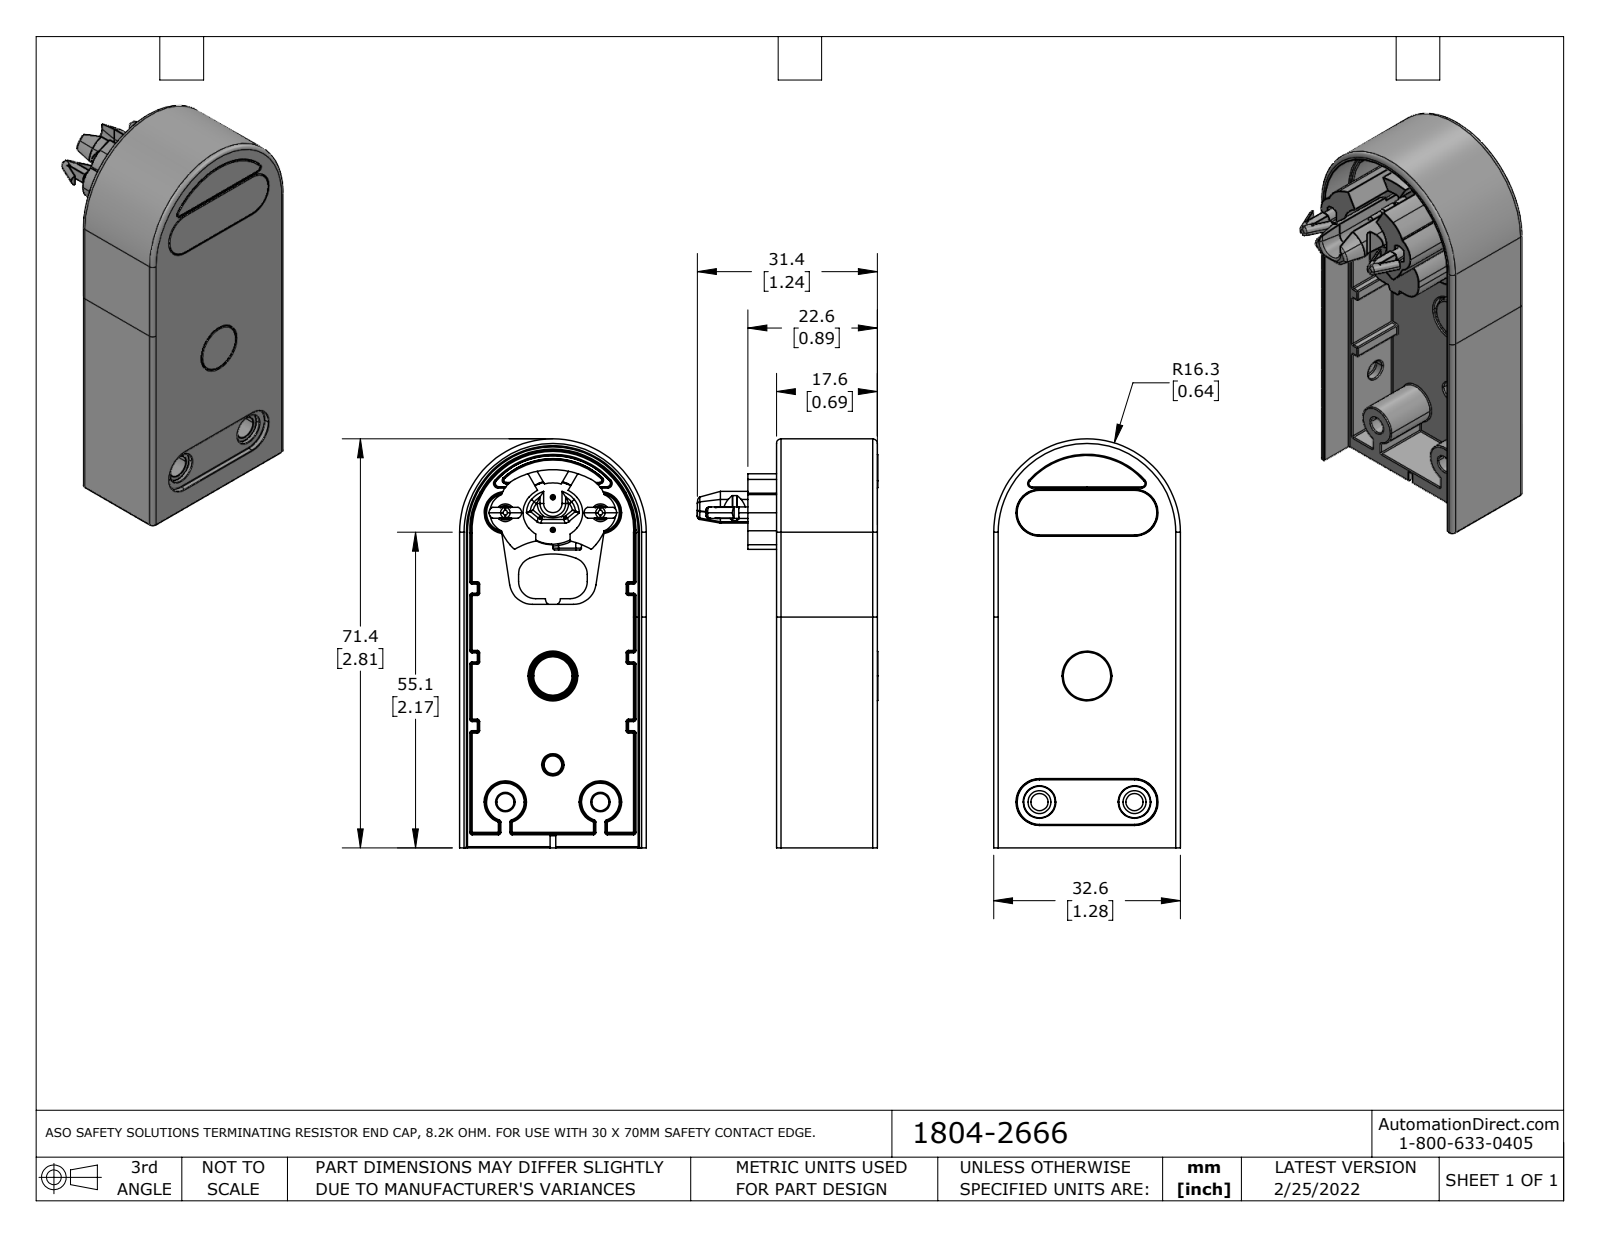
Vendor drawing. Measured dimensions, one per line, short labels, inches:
name: 1804-2666_Default
written by: SolidWorks 2021 (CONFIG_CONTROL_DESIGN)
unit: in
bodies: 6 solids, 804 faces (190 planar, 353 cylindrical, 261 other)
size: 2.811 × 1.283 × 1.24
volume: 0.894 in³; area: 25.98 in²
holes: 4× ⌀0.02, 4× ⌀0.217, 3× ⌀0.138, 3× ⌀0.157, 2× ⌀0.028, 2× ⌀0.118, 2× ⌀0.122, 1× ⌀0.031, 1× ⌀0.157
bosses: 2× ⌀0.276, 2× ⌀0.197, 2× ⌀0.138, 2× ⌀0.098, 2× ⌀0.079, 2× ⌀0.065, 2× ⌀0.035, 2× ⌀0.024
rounds: 75× R0.008, 17× R0.004, 12× R0.039, 6× R0.012, 6× R0.118, 6× R0.138, 6× R0.157, 5× R0.02
face distances: 0.071, 0.031, 0.079, 1.283, 1.205, 0.047, 1.236, 1.157, 0.039, 1.126
hole spacings: 0.654, 0.055, 0.344, 0.348, 0.415, 0.769, 0.792, 0.924
